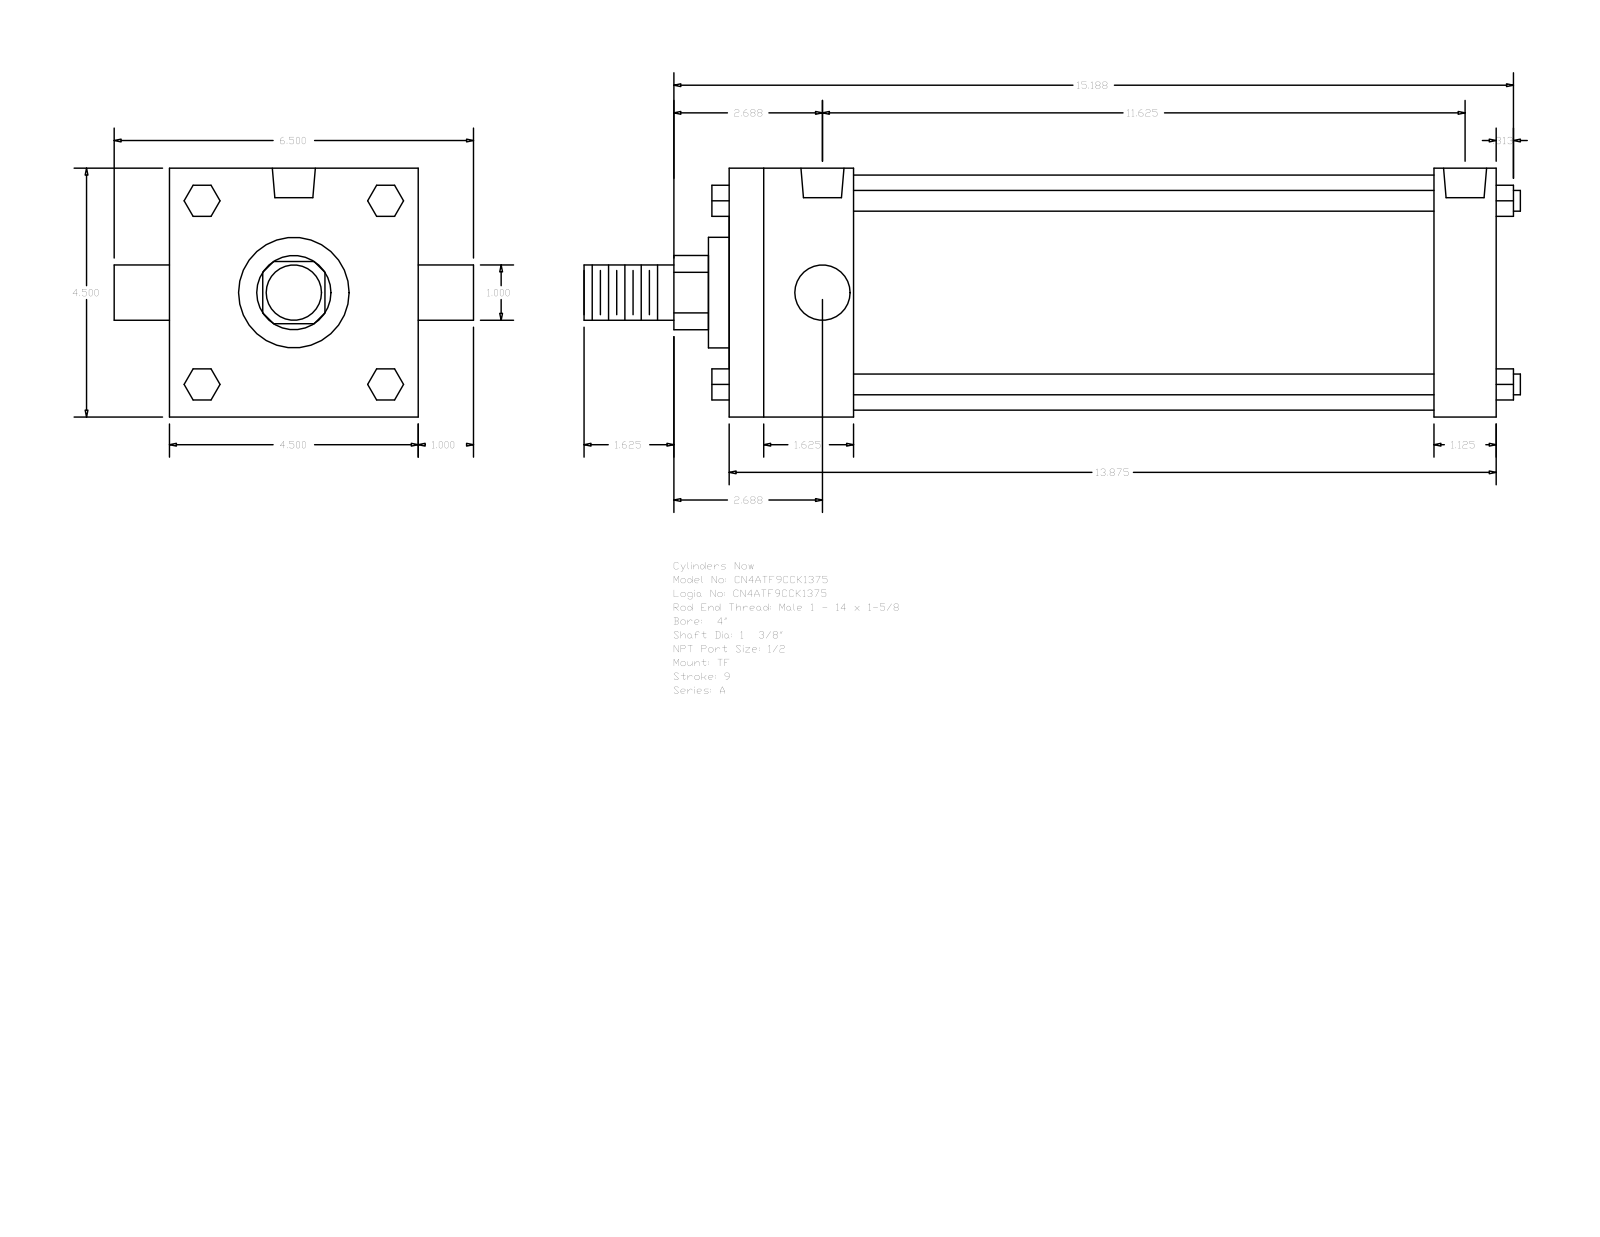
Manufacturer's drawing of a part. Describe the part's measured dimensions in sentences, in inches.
The part is named "A_TF__0400_1.375". Its 3-D file was written by "GSSL Pune (CONFIG_CONTROL_DESIGN)". It is 0 solids with 120 faces: 92 planar, 28 cylindrical and 0 other. Overall it measures 16.937 by 6.5 by 4.5 inches. Round holes: 3 of diameter 0.344, 2 of diameter 0.778. Round bosses or shafts: 4 of diameter 0.375, 2 of diameter 1, 1 of diameter 4.25, 1 of diameter 2, 1 of diameter 1.375. Partial cylindrical surfaces (rounded edges, fillets, slot ends): 1 of radius 0.672. The main face-to-face distances are 4.5, 13.875, 2.25, 12.75, 1.125, 10.5, 11.625, 2.625, 0.563, 1. The hole center spacings are 0.125, 11.5, 11.375, 11.625.
